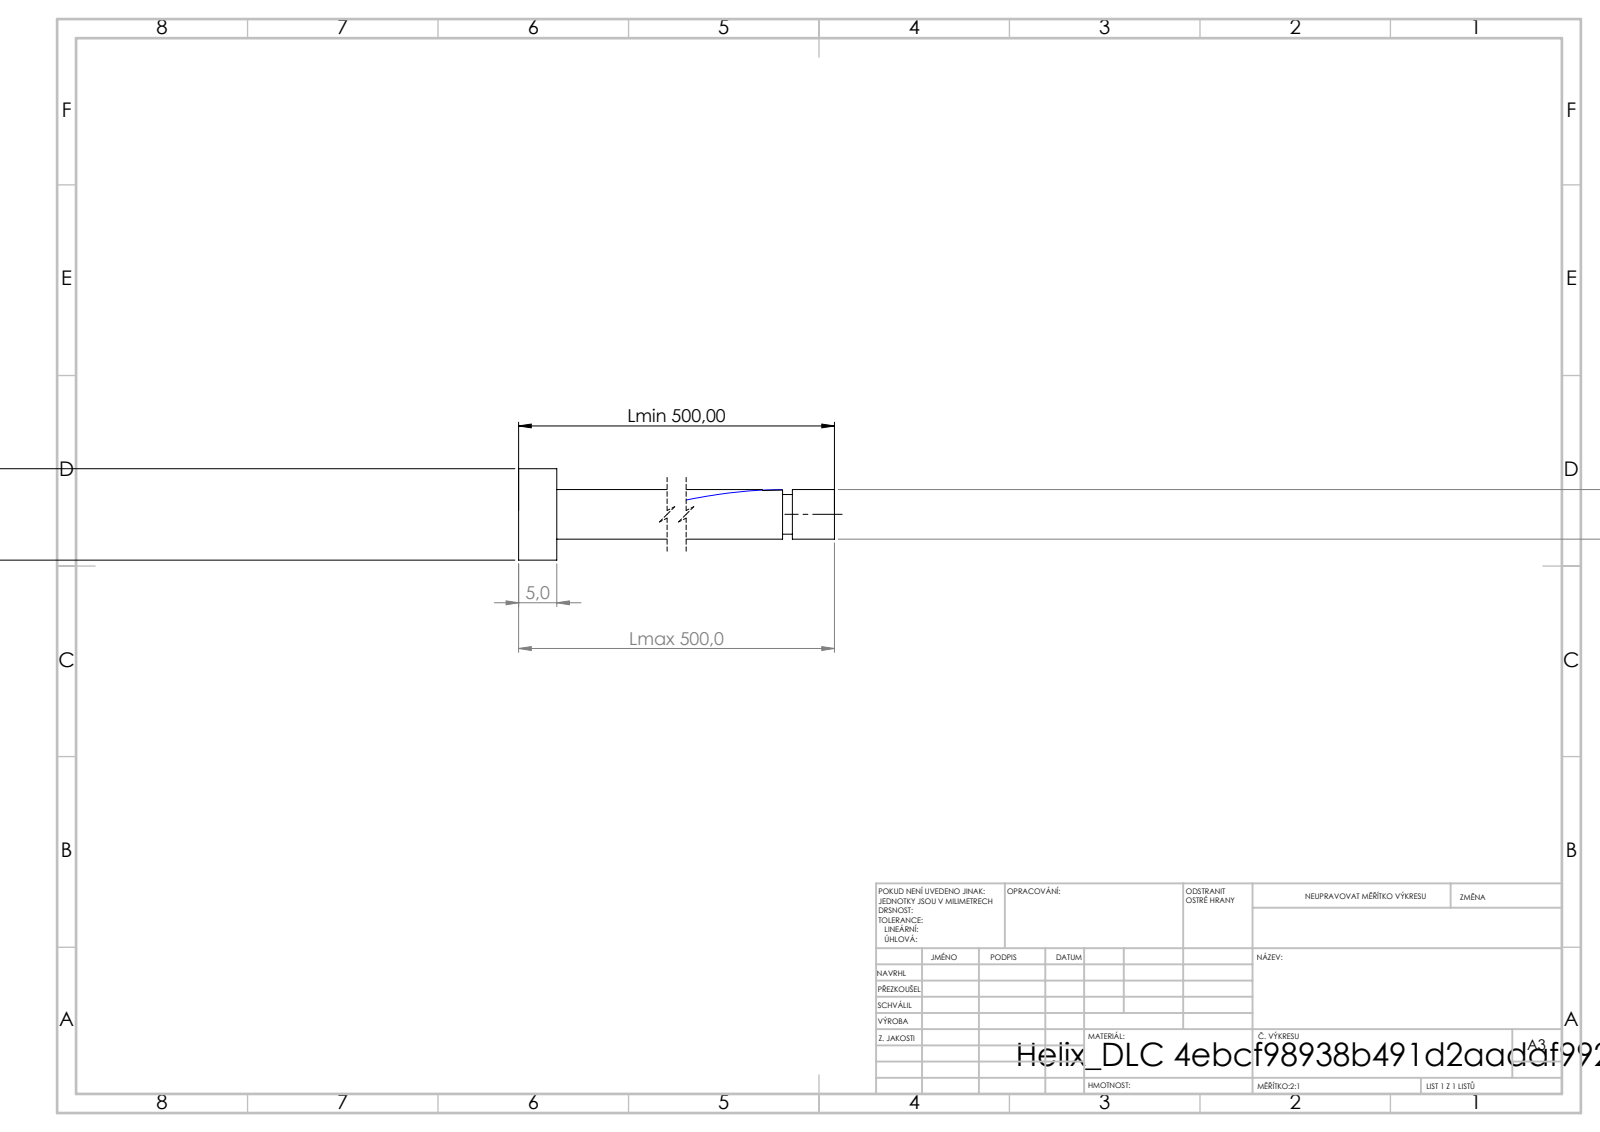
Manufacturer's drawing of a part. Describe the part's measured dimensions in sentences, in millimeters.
Its 3-D file was written by "SolidWorks 2019 (CONFIG_CONTROL_DESIGN)". It is 1 solid with 16 faces: 6 planar, 9 cylindrical and 1 other. Overall it measures 500 by 12 by 12 millimeters. Its volume is 20 503 cubic millimeters and its surface area 14 103 square millimeters. Round bosses or shafts: 1 of diameter 12, 1 of diameter 6.5, 1 of diameter 5.2. The main face-to-face distances are 5, 500, 495, 494.48, 489.48, 5.52, 493.18, 488.18, 1.3, 6.82.
